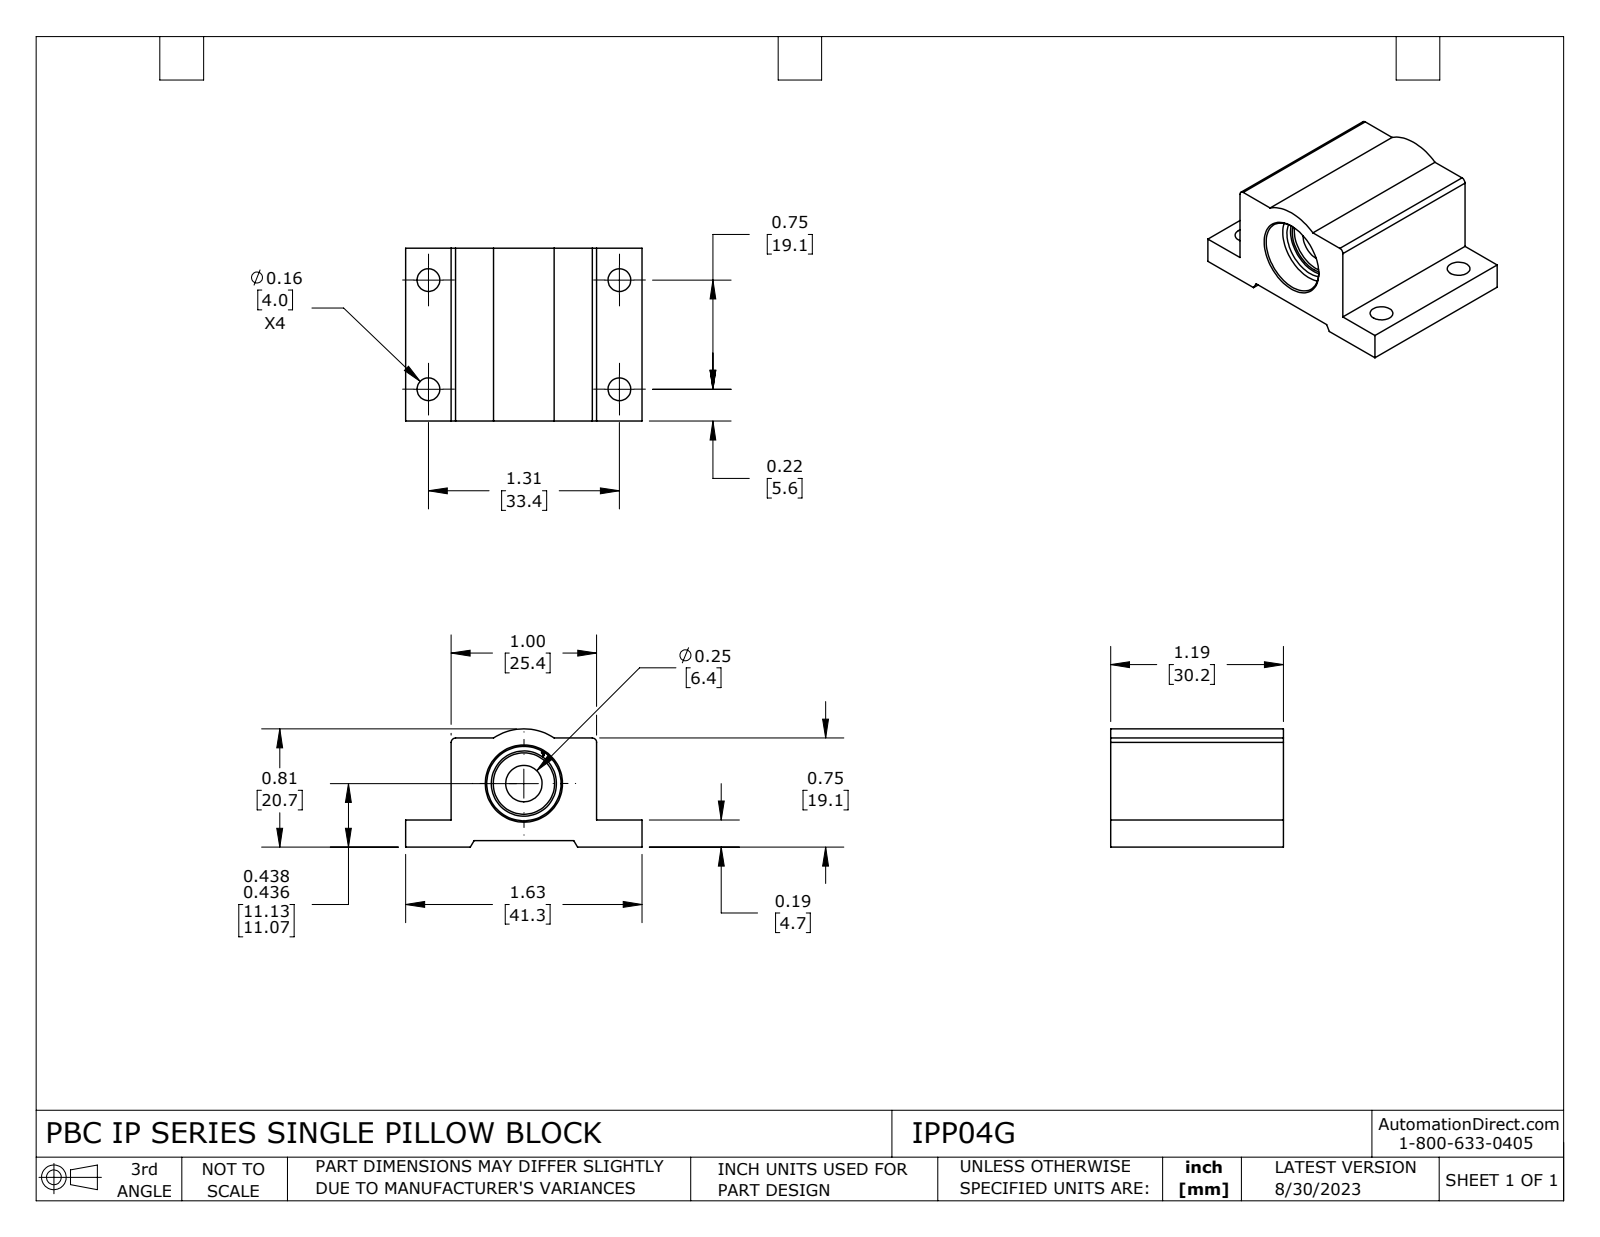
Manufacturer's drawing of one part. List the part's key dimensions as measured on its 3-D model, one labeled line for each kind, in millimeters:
Part name (STEP PRODUCT): IPP04G
STEP written by: SolidWorks 2021 (CONFIG_CONTROL_DESIGN)
Units: millimetres
Bodies: 4 solids, 126 faces (43 planar, 63 cylindrical, 20 other)
Overall size (bounding box): 41.3 × 30.1 × 20.7
Volume: 14 200 mm³ · Surface area: 7 613 mm²
Round holes (diameter × count): ⌀4 ×4, ⌀6.4 ×1, ⌀10.7 ×1, ⌀11.4 ×1, ⌀13 ×1, ⌀13.5 ×1
Round bosses / shafts (diameter × count): ⌀13.7 ×1, ⌀12.7 ×1, ⌀11.9 ×1
Partial cylindrical surfaces — rounded edges, fillets, slot ends (radius × count): R0.2 ×4, R0.3 ×2, R0.8 ×2, R9.6 ×1
Main face-to-face distances: 1.1, 4.7, 3.6, 25.4, 30.1, 19.1, 17.9, 14.3, 8, 33.4
Hole centre spacings: 19.1, 33.4, 38.4
